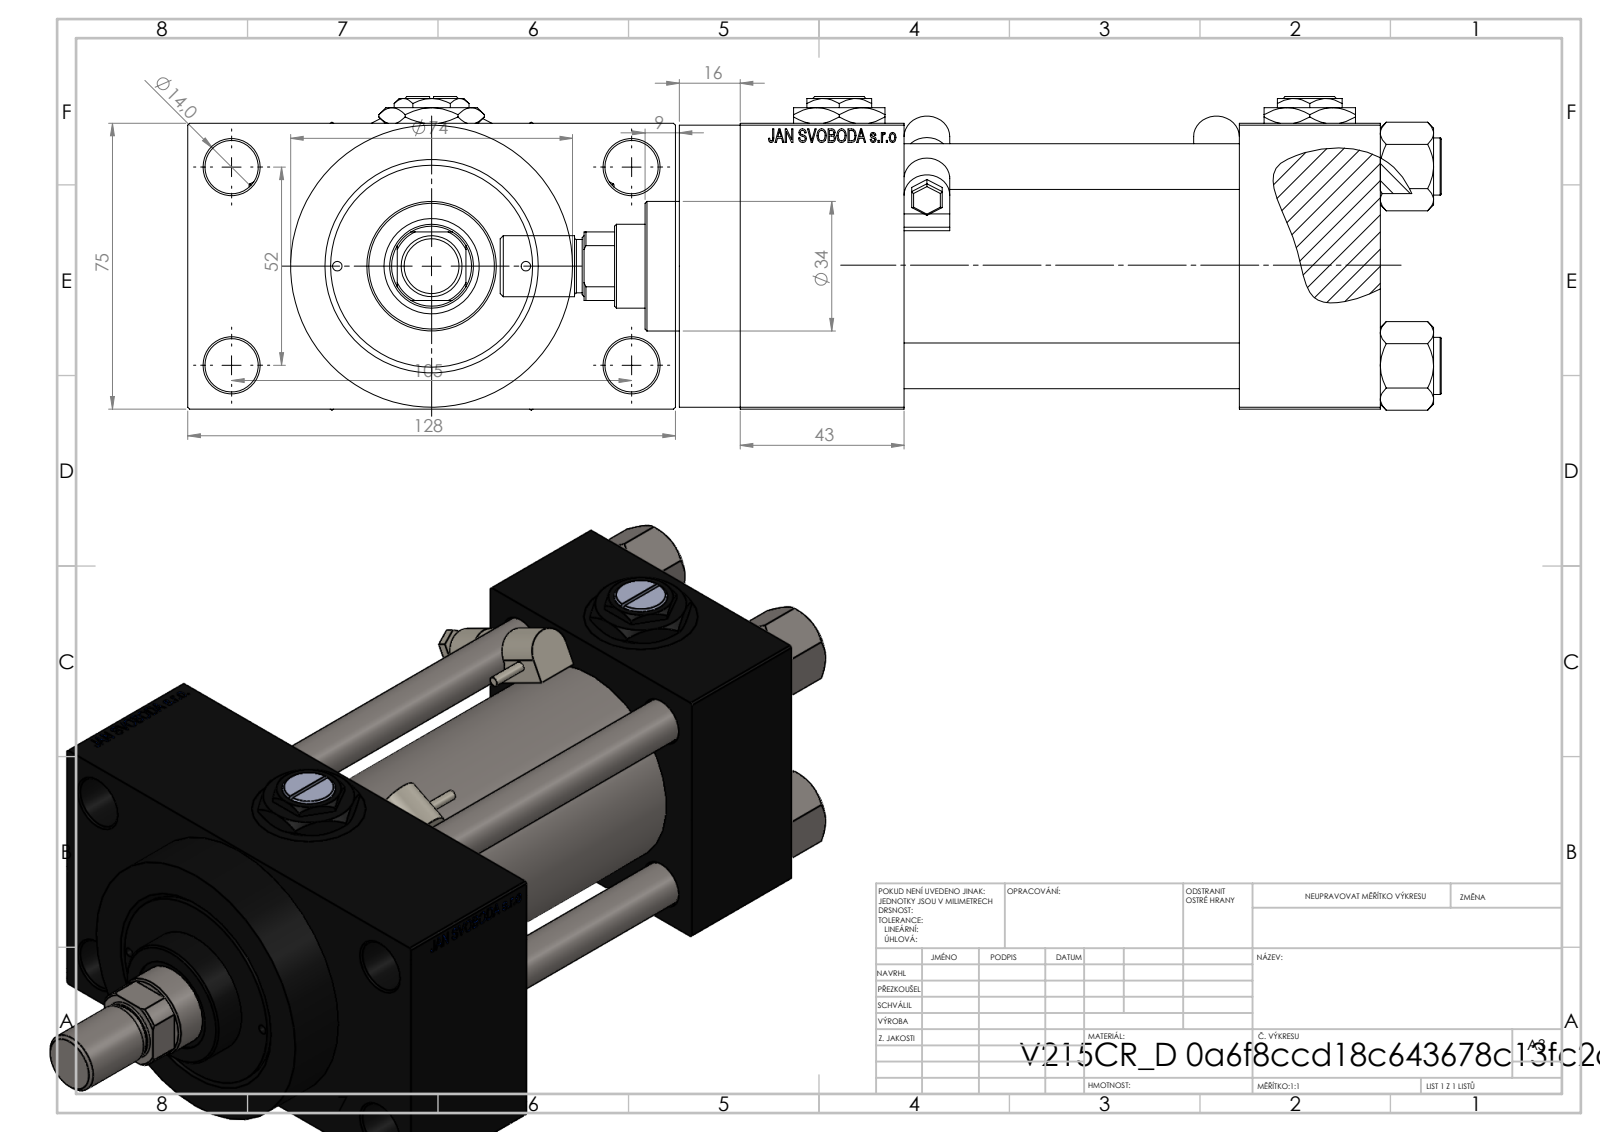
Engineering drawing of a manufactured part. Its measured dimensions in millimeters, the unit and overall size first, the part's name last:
Units: millimetres
Overall size (bounding box): 247 × 128 × 82.27
Round holes (diameter × count): ⌀12 ×4, ⌀14 ×4, ⌀2.5 ×2, ⌀7 ×2, ⌀20.96 ×2, ⌀30 ×2, ⌀10.5 ×1, ⌀22 ×1, ⌀25 ×1, ⌀41 ×1, ⌀50 ×1, ⌀53 ×1
Round bosses / shafts (diameter × count): ⌀15 ×4, ⌀5 ×2, ⌀2.5 ×2, ⌀74 ×1, ⌀56 ×1, ⌀34 ×1, ⌀16 ×1, ⌀14 ×1
Partial cylindrical surfaces — rounded edges, fillets, slot ends (radius × count): R0.5 ×12, R6 ×4, R10.5 ×1
Main face-to-face distances: 75, 88, 37, 125, 26.5, 101.5, 168, 131, 43, 16
Hole centre spacings: 26.19, 26.35, 36.98, 38.03, 52.3, 57.22, 58.43, 58.59
Volume: 853 584 mm³ · Surface area: 191 741 mm²
Bodies: 16 solids, 1291 faces (587 planar, 136 cylindrical, 568 other)
Part name (STEP PRODUCT): V215CR_D_Body; NUT_M5_D; Zatka_pro_OIL_PORT; V215_VC_A (+4 more)
STEP written by: SolidWorks 2019 (CONFIG_CONTROL_DESIGN)
